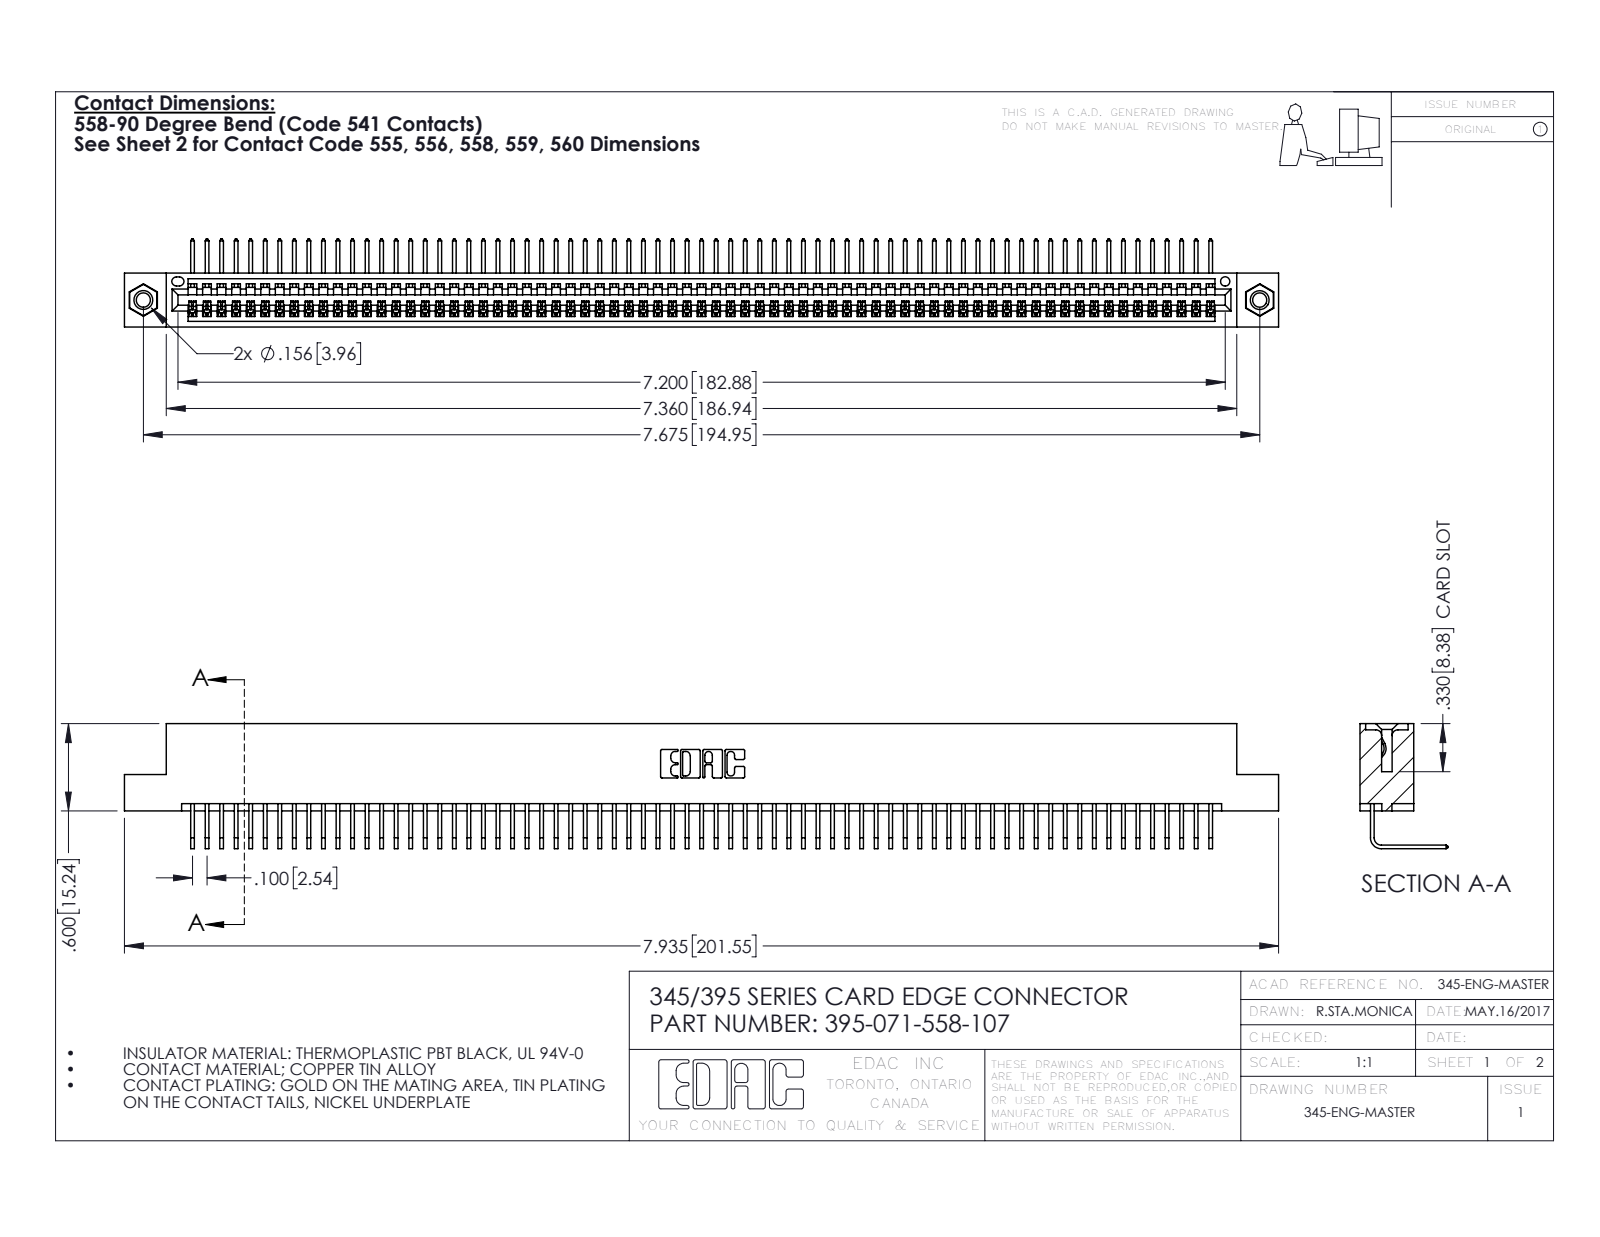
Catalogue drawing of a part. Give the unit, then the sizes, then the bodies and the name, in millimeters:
Units: millimetres
Overall size (bounding box): 201.5 × 21.8 × 15.4
Round holes (diameter × count): ⌀2.5 ×2, ⌀3.2 ×2, ⌀4 ×2, ⌀1.6 ×1
Round bosses / shafts (diameter × count): ⌀3.9 ×2
Partial cylindrical surfaces — rounded edges, fillets, slot ends (radius × count): R0.2 ×142, R0.3 ×22, R0.2 ×6, R0.8 ×6, R0.7 ×3, R0.8 ×2, R1 ×2, R0.4 ×1
Main face-to-face distances: 1.8, 7.6, 9.4, 5.1, 2.5, 6.9, 0.6, 5.7, 3.8, 1.8
Hole centre spacings: 6.9, 189, 194.9
Volume: 19 600 mm³ · Surface area: 27 870 mm²
Bodies: 74 solids, 4446 faces (3094 planar, 1336 cylindrical, 16 other)
Part name (STEP PRODUCT): 345-250-001_345-250-005-103; 395-071-558-107; 345-292-001_558 Tail - 2; 345 Part_Flush Mounting Lugs - 0.156 Dia-TI
STEP written by: SolidWorks 2016 (CONFIG_CONTROL_DESIGN)
